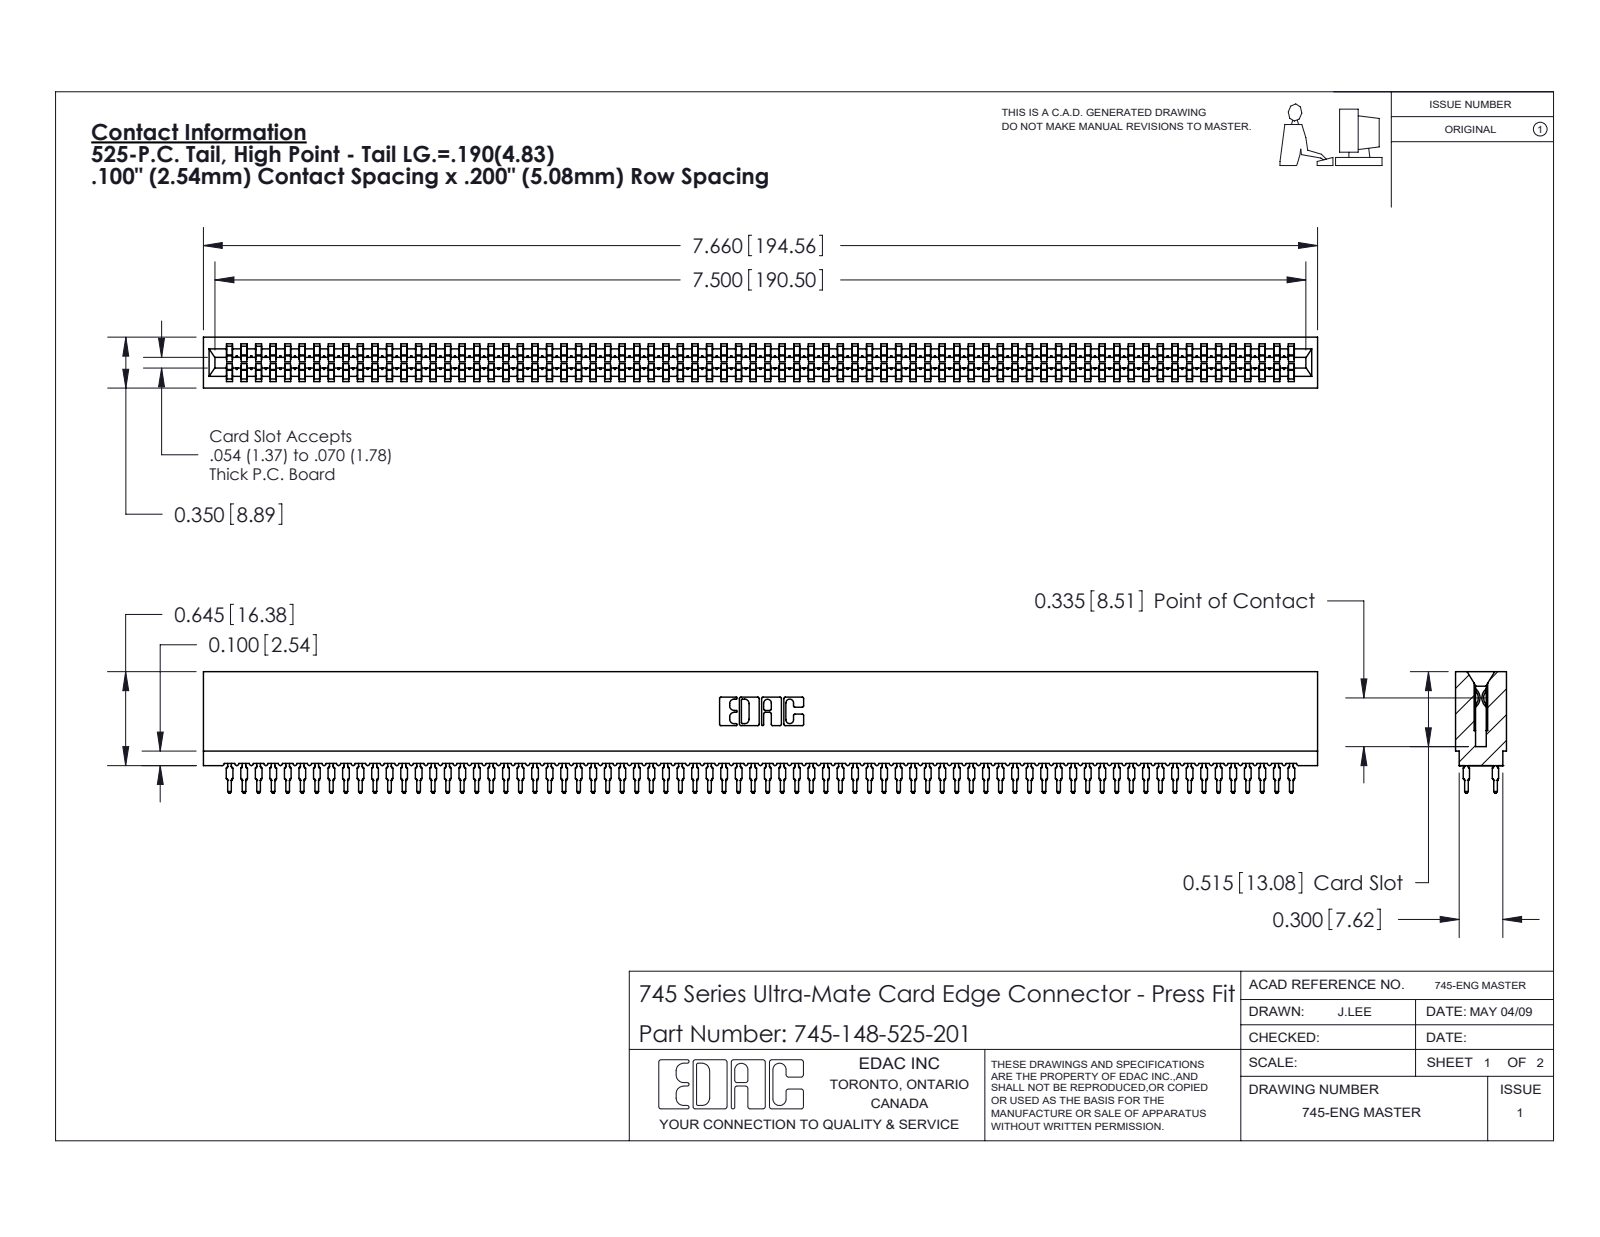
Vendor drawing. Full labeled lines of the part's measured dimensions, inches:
Part name (STEP PRODUCT): 745-292-001_525; 745 Part_Insulator Option - 01; 745-148-525-201
STEP written by: SolidWorks 2020 (CONFIG_CONTROL_DESIGN)
Units: inches
Bodies: 149 solids, 13341 faces (6863 planar, 2630 cylindrical, 3848 other)
Overall size (bounding box): 7.66 × 0.836 × 0.35
Volume: 1.055 in³ · Surface area: 55.41 in²
Partial cylindrical surfaces — rounded edges, fillets, slot ends (radius × count): R0.021 ×296, R0.015 ×148, R0.01 ×22, R0.005 ×8, R0.011 ×8, R0.007 ×6, R0.031 ×6, R0.026 ×3
Main face-to-face distances: 0.35, 0.063, 0.287, 0.045, 0.305, 0.018, 0.243, 0.138, 0.212, 0.093
